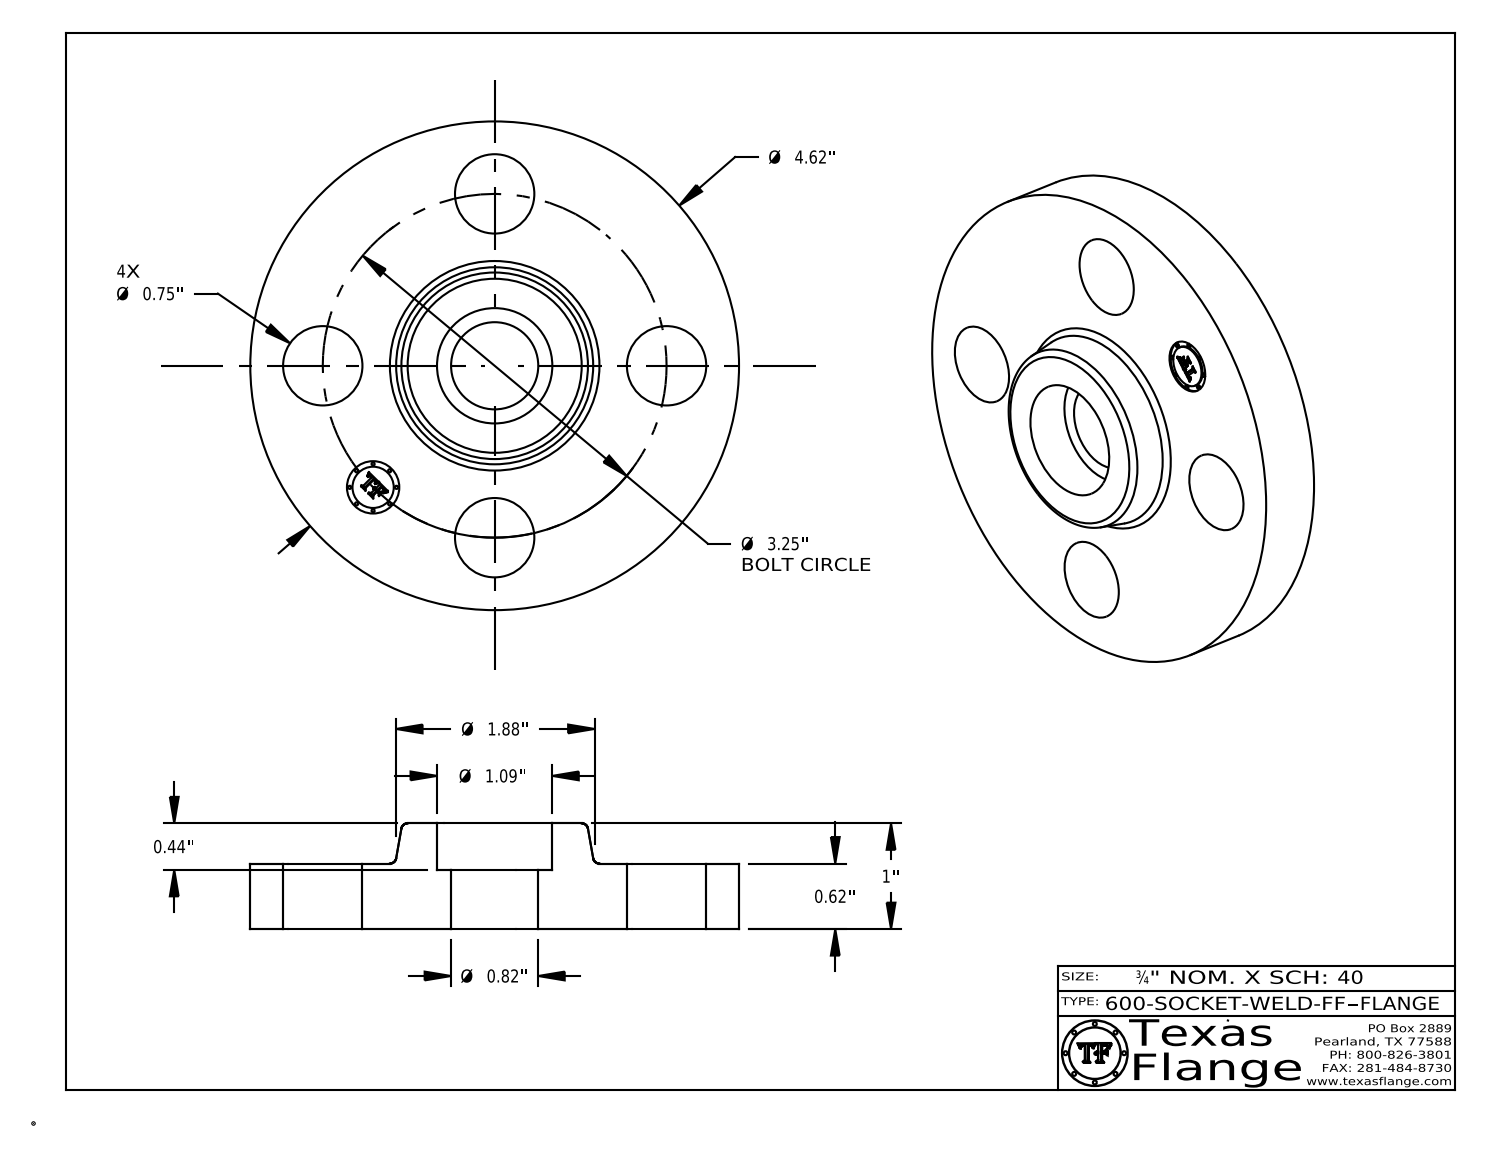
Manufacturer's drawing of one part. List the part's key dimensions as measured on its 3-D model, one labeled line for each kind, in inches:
Part name (STEP PRODUCT): 600-SOCKET-WELD-FF
STEP written by: CATIA V5 STEP AP214 (AUTOMOTIVE_DESIGN)
Units: inches
Bodies: 1 solid, 409 faces (369 planar, 34 cylindrical, 6 other)
Overall size (bounding box): 4.62 × 4.62 × 1
Volume: 9.569 in³ · Surface area: 48.44 in²
Round holes (diameter × count): ⌀0.75 ×4, ⌀0.495 ×1, ⌀0.824 ×1, ⌀1.09 ×1
Round bosses / shafts (diameter × count): ⌀0.03 ×8, ⌀4.62 ×1, ⌀0.39 ×1
Main face-to-face distances: 0.62, 1, 0.38, 0.56, 0.06, 0.44, 0.605, 0.045, 0.015, 0.395
Hole centre spacings: 1.625, 2.298, 1.244, 3.003, 3.25
